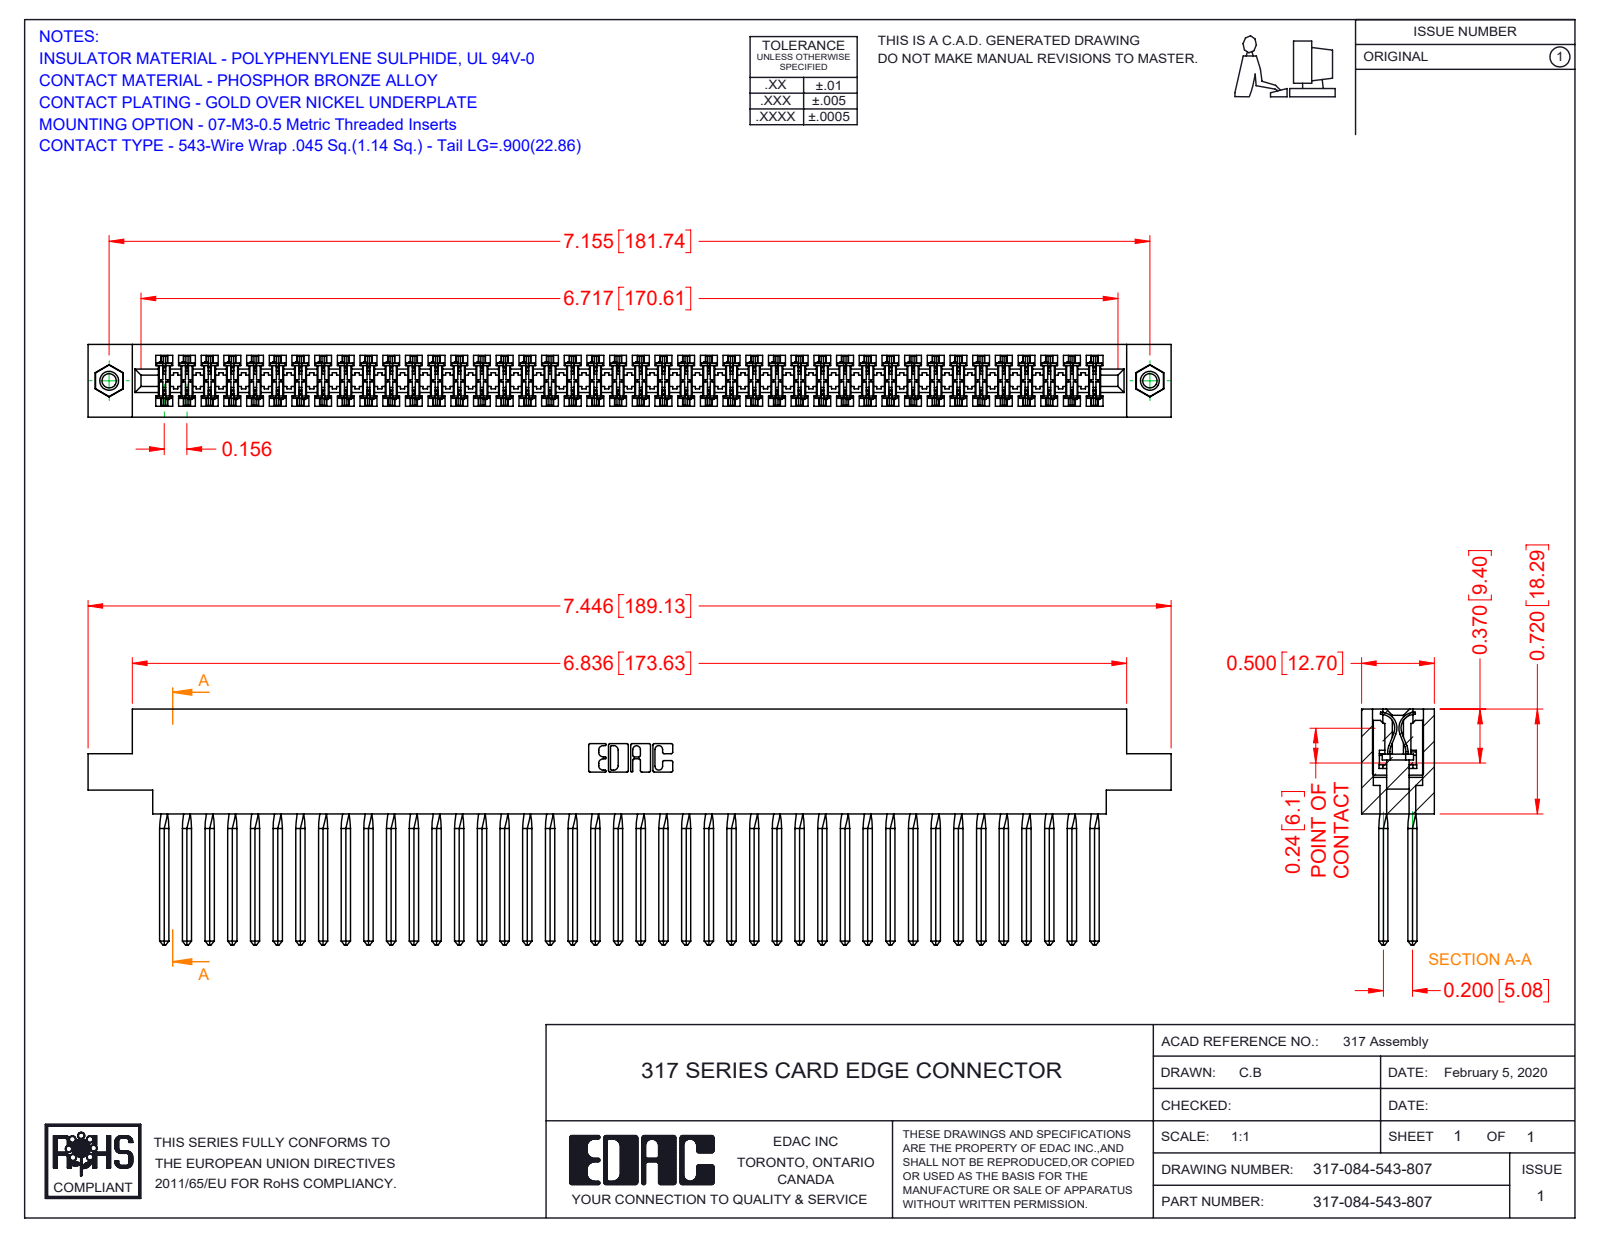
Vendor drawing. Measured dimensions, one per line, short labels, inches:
name: 317 Part_.156 Dia - TI; 317-084-543-807; 317-290-001_543; 345-250-001_345-250-005-103
written by: SolidWorks 2016 (CONFIG_CONTROL_DESIGN)
unit: in
bodies: 87 solids, 7638 faces (6222 planar, 1064 cylindrical, 352 other)
size: 7.446 × 1.62 × 0.5
volume: 1.962 in³; area: 75.65 in²
holes: 2× ⌀0.098, 2× ⌀0.125, 2× ⌀0.156
bosses: 2× ⌀0.155
rounds: 168× R0.015, 22× R0.01, 6× R0.007, 6× R0.031, 3× R0.026, 2× R0.095, 2× R0.1, 2× R0.11
face distances: 0.5, 0.075, 0.425, 0.35, 0.195, 0.11, 0.094, 0.2, 0.115, 0.131
hole spacings: 7.155
